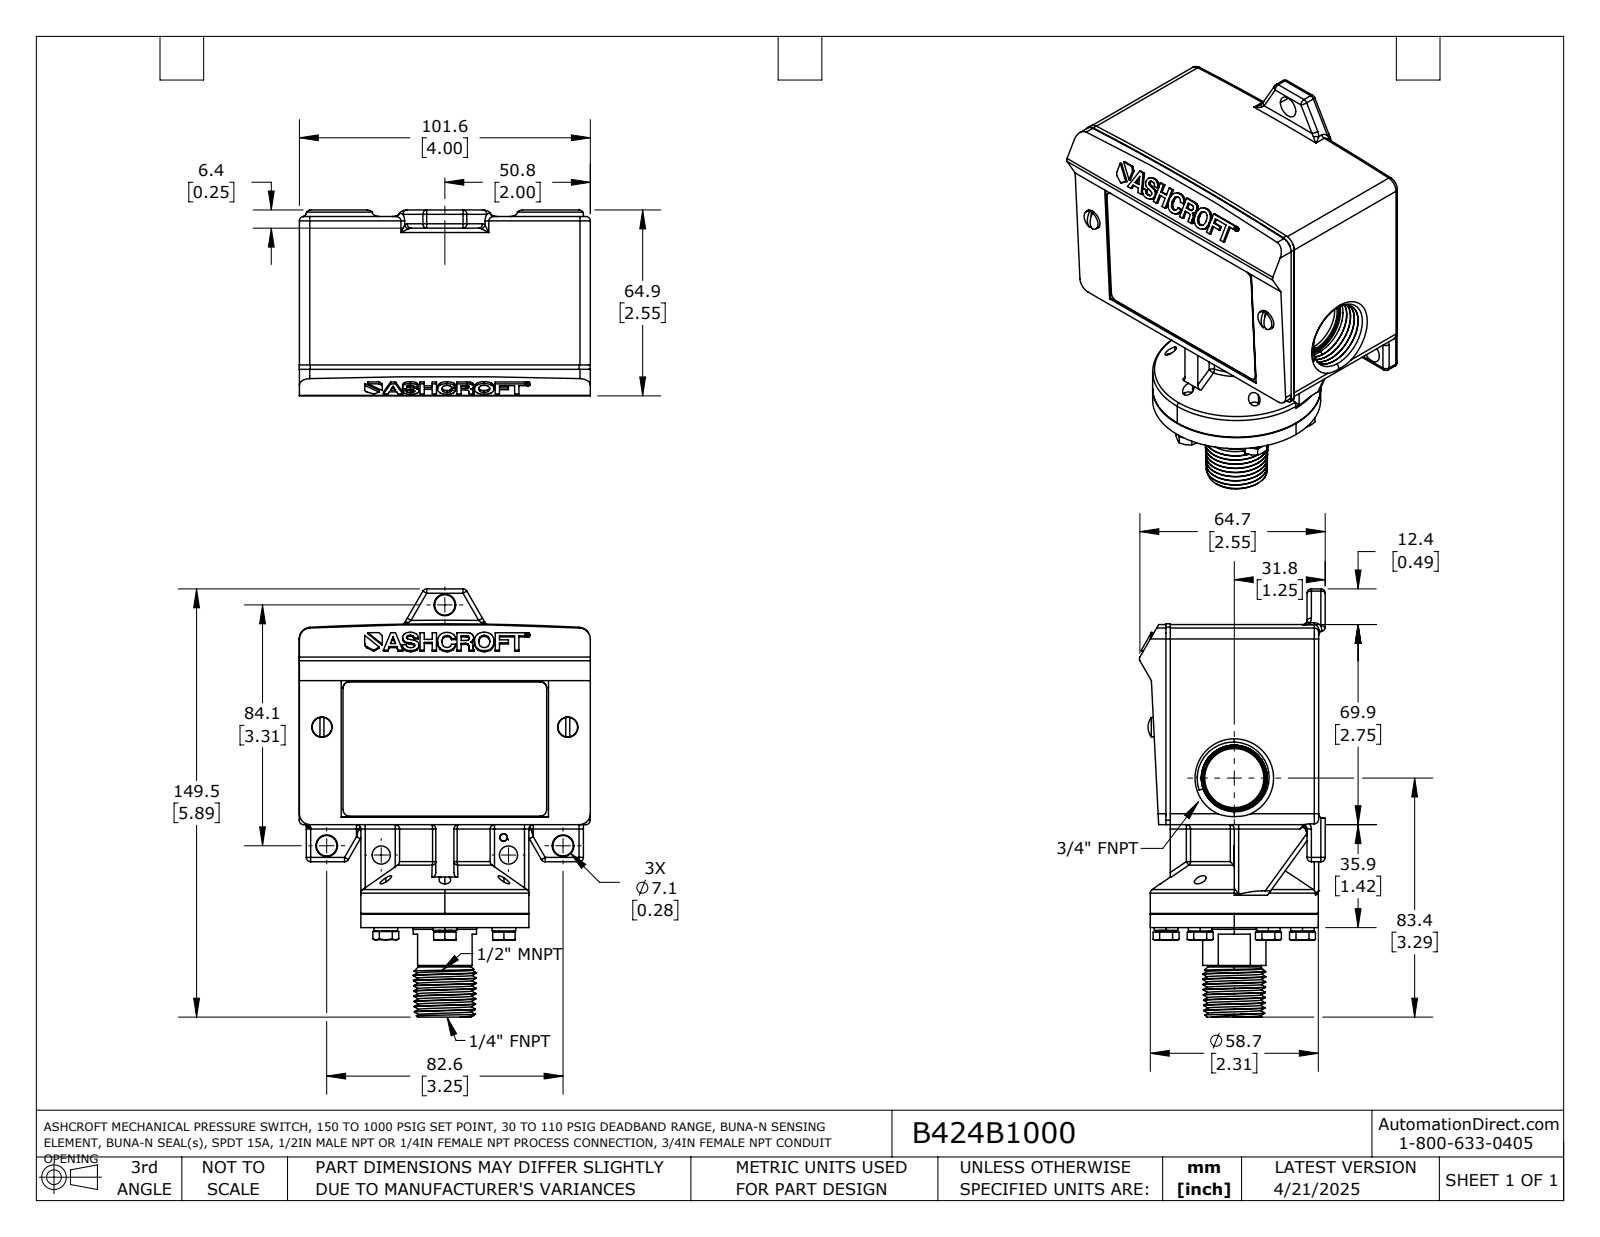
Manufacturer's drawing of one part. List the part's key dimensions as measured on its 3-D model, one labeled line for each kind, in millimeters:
Part name (STEP PRODUCT): B424B1000
STEP written by: SolidWorks 2021 (AUTOMOTIVE_DESIGN)
Units: millimetres
Bodies: 1 solid, 1203 faces (301 planar, 478 cylindrical, 424 other)
Overall size (bounding box): 149.5 × 101.7 × 64.9
Volume: 476 200 mm³ · Surface area: 57 540 mm²
Round holes (diameter × count): ⌀4.1 ×6, ⌀4.7 ×5, ⌀4.9 ×5, ⌀5.3 ×5, ⌀7.1 ×2, ⌀20.6 ×1
Round bosses / shafts (diameter × count): ⌀8.3 ×6, ⌀7.1 ×6, ⌀4.8 ×5, ⌀6.9 ×2, ⌀6.4 ×2, ⌀58.7 ×1, ⌀22.1 ×1
Partial cylindrical surfaces — rounded edges, fillets, slot ends (radius × count): R1.5 ×92, R2.3 ×4, R3.8 ×4, R4.1 ×2, R15.9 ×2, R914.4 ×2, R0.8 ×1, R1.3 ×1
Main face-to-face distances: 101.6, 35.9, 0.4, 2.3, 99.3, 11.2, 90.4, 88.1, 8.9, 21.5
Hole centre spacings: 41.2, 23.8, 47.6, 23.8, 85.9
